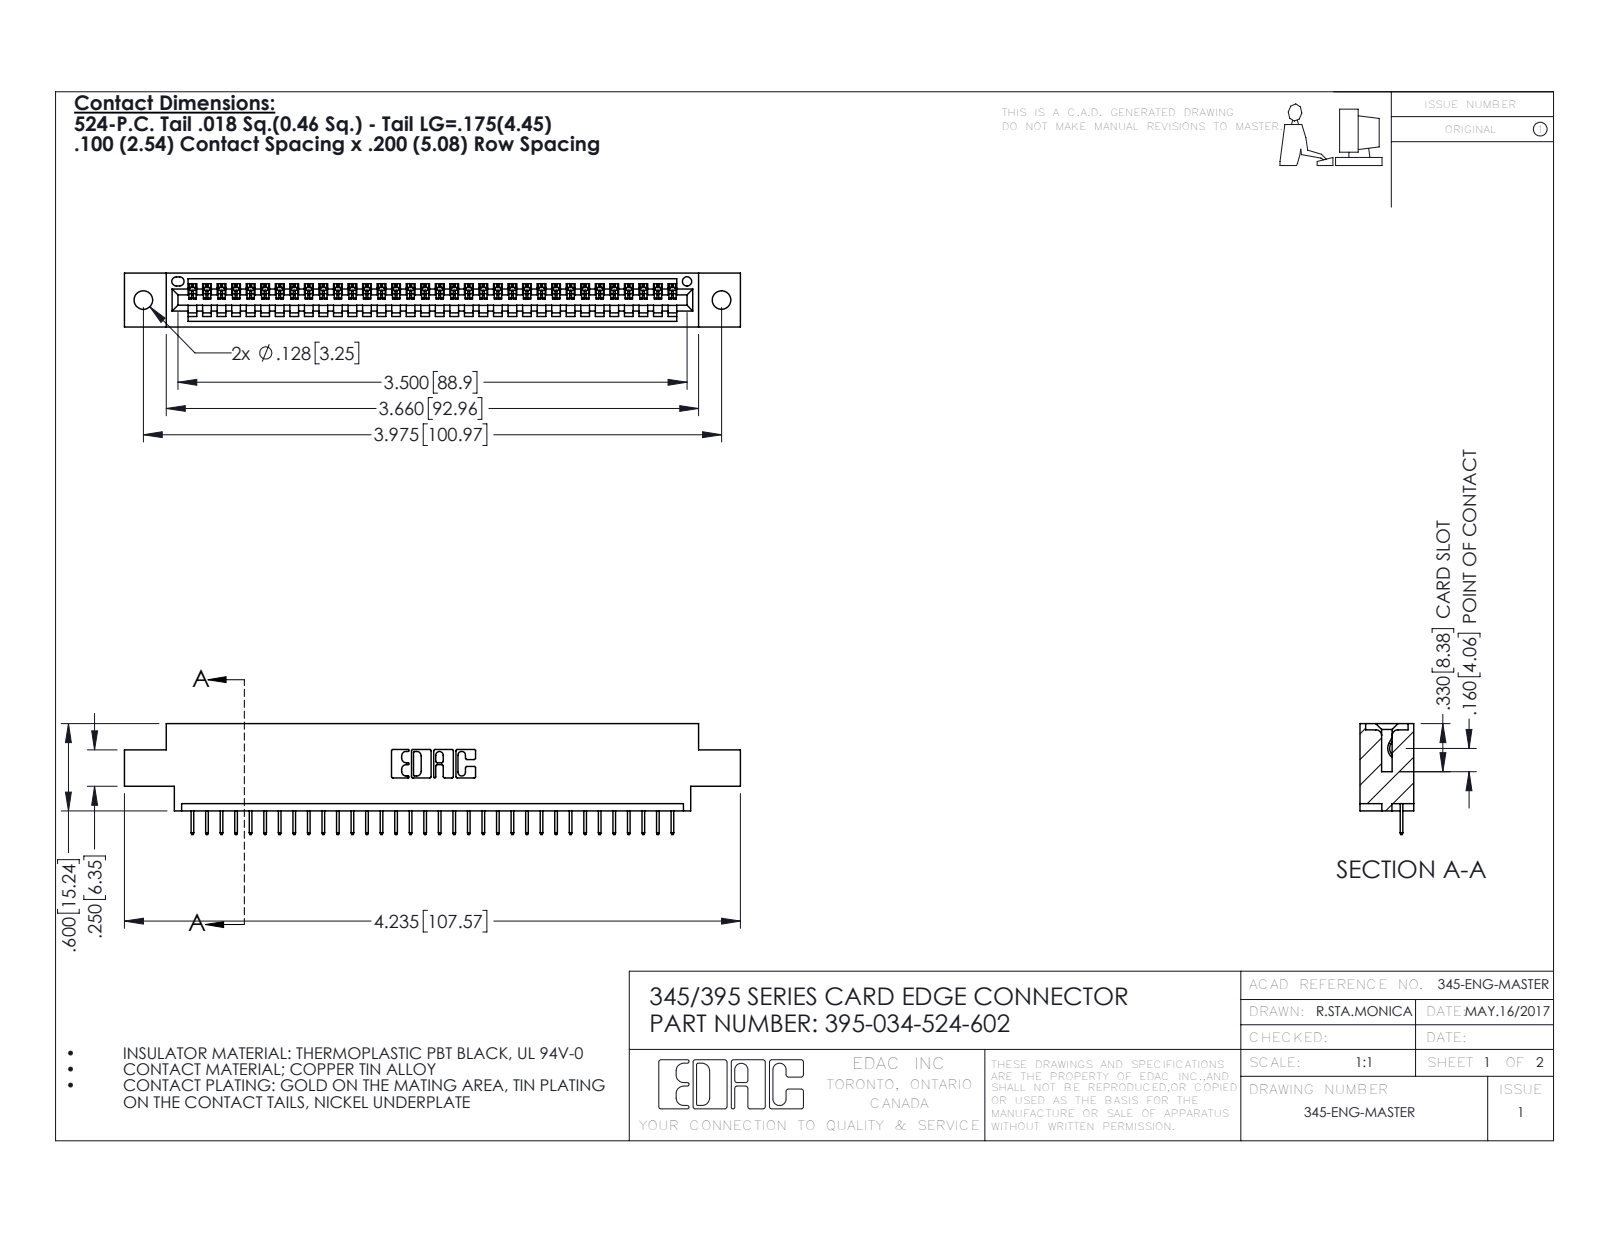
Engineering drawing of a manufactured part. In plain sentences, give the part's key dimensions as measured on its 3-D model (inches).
The part is named "345 Part_0.170 Offset - 0.128 Dia; 345-292-001_345-293-124; 395-034-524-602". Its 3-D file was written by "SolidWorks 2016 (CONFIG_CONTROL_DESIGN)". It is 35 solids with 2238 faces: 1648 planar, 590 cylindrical and 0 other. Overall it measures 4.235 by 0.762 by 0.37 inches. Its volume is 0.602 cubic inches and its surface area 19.27 square inches. Round holes: 2 of diameter 0.128, 1 of diameter 0.064. Partial cylindrical surfaces (rounded edges, fillets, slot ends): 68 of radius 0.006, 22 of radius 0.01, 6 of radius 0.007, 6 of radius 0.031, 3 of radius 0.026, 2 of radius 0.031, 2 of radius 0.04, 1 of radius 0.014. The main face-to-face distances are 0.072, 0.298, 0.37, 0.2, 0.098, 0.272, 0.025, 0.225, 0.072, 0.175. The hole center spacings are 0.27, 3.74, 3.975.
